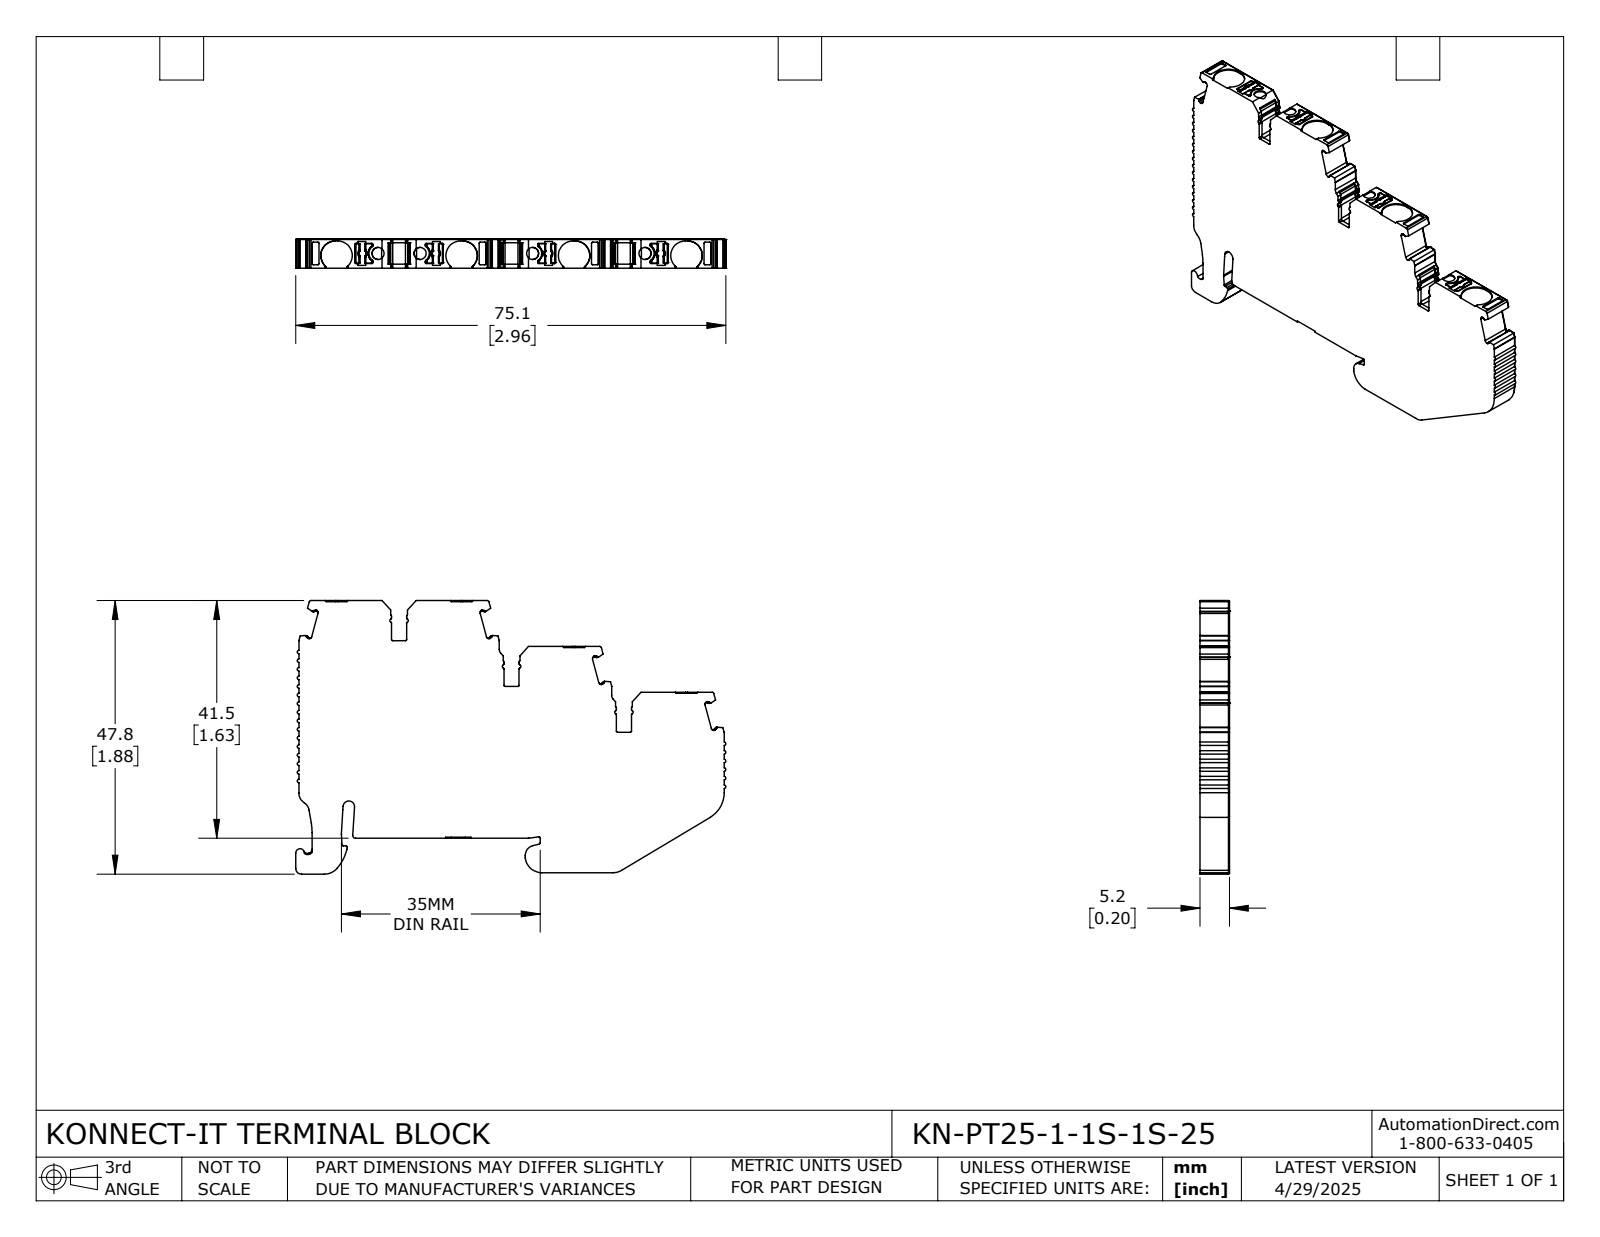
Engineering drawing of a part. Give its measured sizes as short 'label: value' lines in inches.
name: KN-PT25-1-1S-1S-25
written by: SolidWorks 2024 (CONFIG_CONTROL_DESIGN)
unit: in
bodies: 1 solid, 936 faces (442 planar, 423 cylindrical, 71 other)
size: 2.957 × 1.88 × 0.203
volume: 0.813 in³; area: 10.75 in²
holes: 4× ⌀0.083
rounds: 92× R0.008, 59× R0.012, 35× R0.004, 16× R0.006, 16× R0.02, 13× R0.016, 8× R0.006, 8× R0.01
face distances: 0.203, 0.315, 0.63, 0.236, 0.63, 0.315, 0.307, 0.323, 0.079, 0.773
hole spacings: 0.289, 0.773, 0.773, 1.062, 1.546, 1.835
